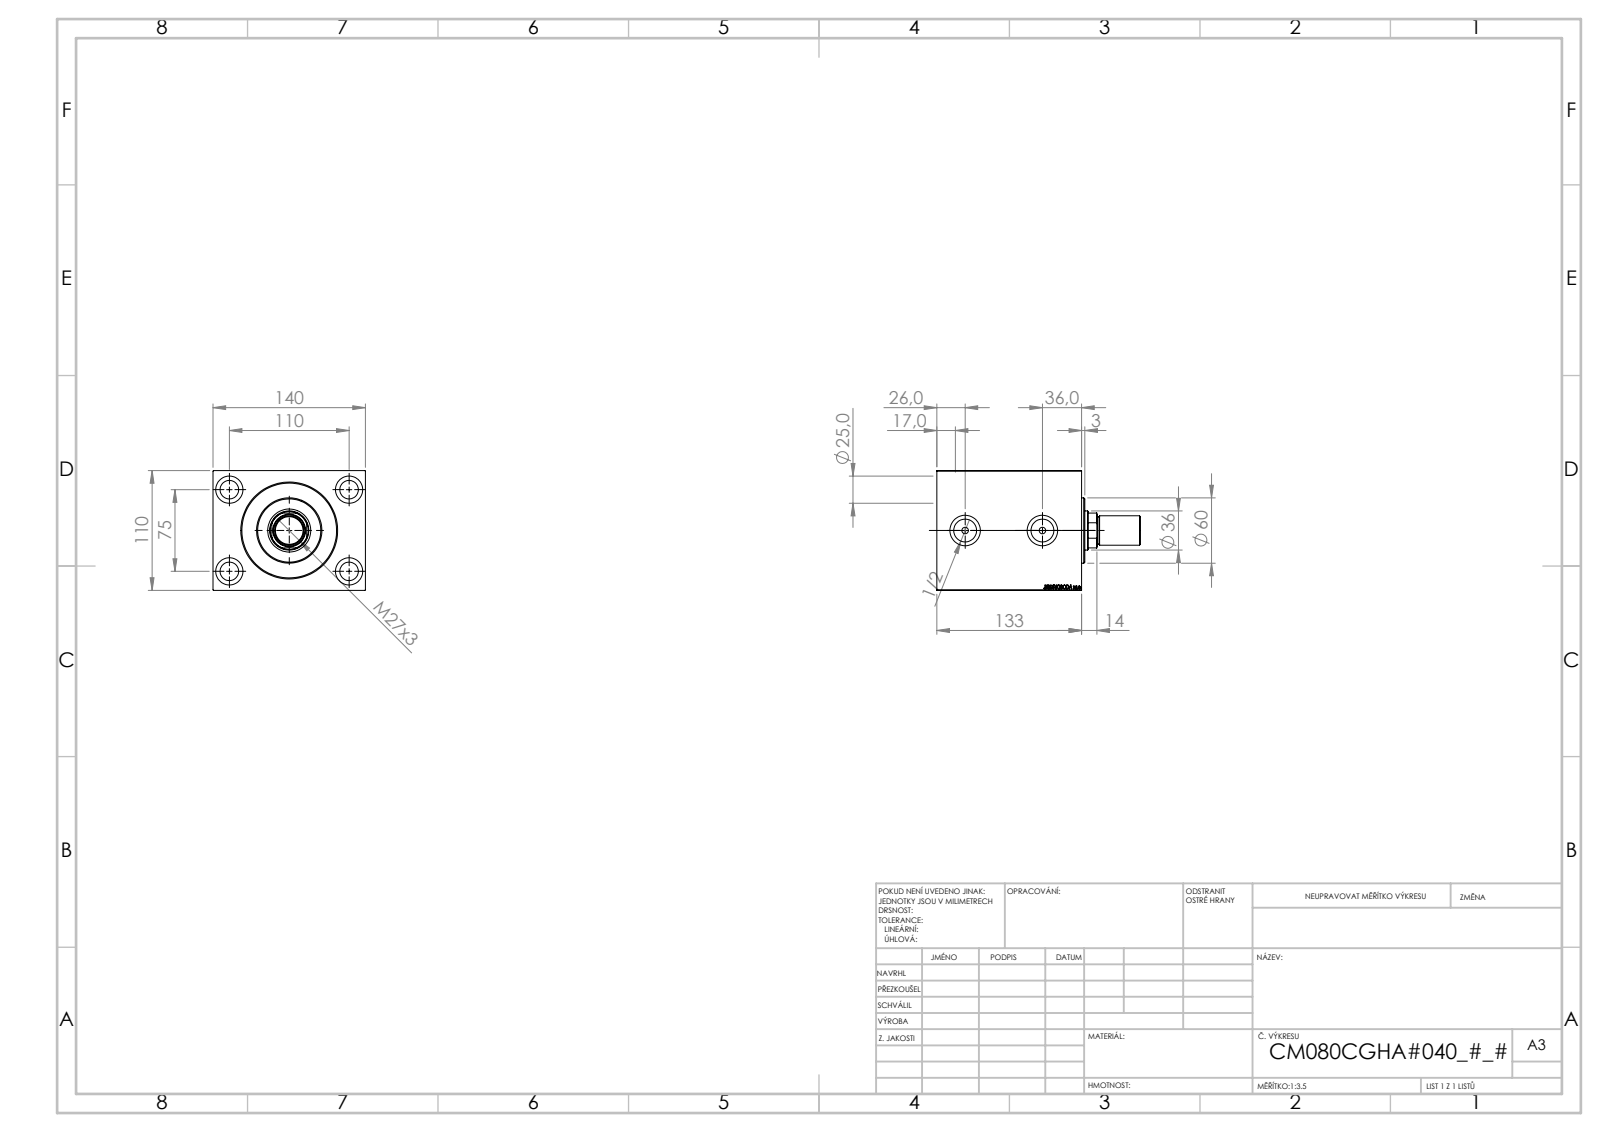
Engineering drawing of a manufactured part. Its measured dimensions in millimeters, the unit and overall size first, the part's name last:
Units: millimetres
Overall size (bounding box): 187 × 140 × 110
Round holes (diameter × count): ⌀17 ×4, ⌀25 ×4, ⌀6 ×2, ⌀20.96 ×2, ⌀28 ×2, ⌀25.5 ×1, ⌀36 ×1, ⌀39.5 ×1, ⌀80 ×1, ⌀82 ×1, ⌀87 ×1
Round bosses / shafts (diameter × count): ⌀60 ×1, ⌀27 ×1, ⌀25 ×1
Partial cylindrical surfaces — rounded edges, fillets, slot ends (radius × count): R17.5 ×1
Main face-to-face distances: 110, 140, 133, 108.5, 24.5, 40, 37.3, 71.2, 95.7, 77.3
Hole centre spacings: 66.57, 75, 110, 133.14, 71
Volume: 1 744 000 mm³ · Surface area: 217 235 mm²
Bodies: 4 solids, 880 faces (414 planar, 66 cylindrical, 400 other)
Part name (STEP PRODUCT): V450CM_C_VCP; V450CM_VC_B; V450CM_MALE_METRIC; V450CM_C_Body
STEP written by: SolidWorks 2019 (CONFIG_CONTROL_DESIGN)
